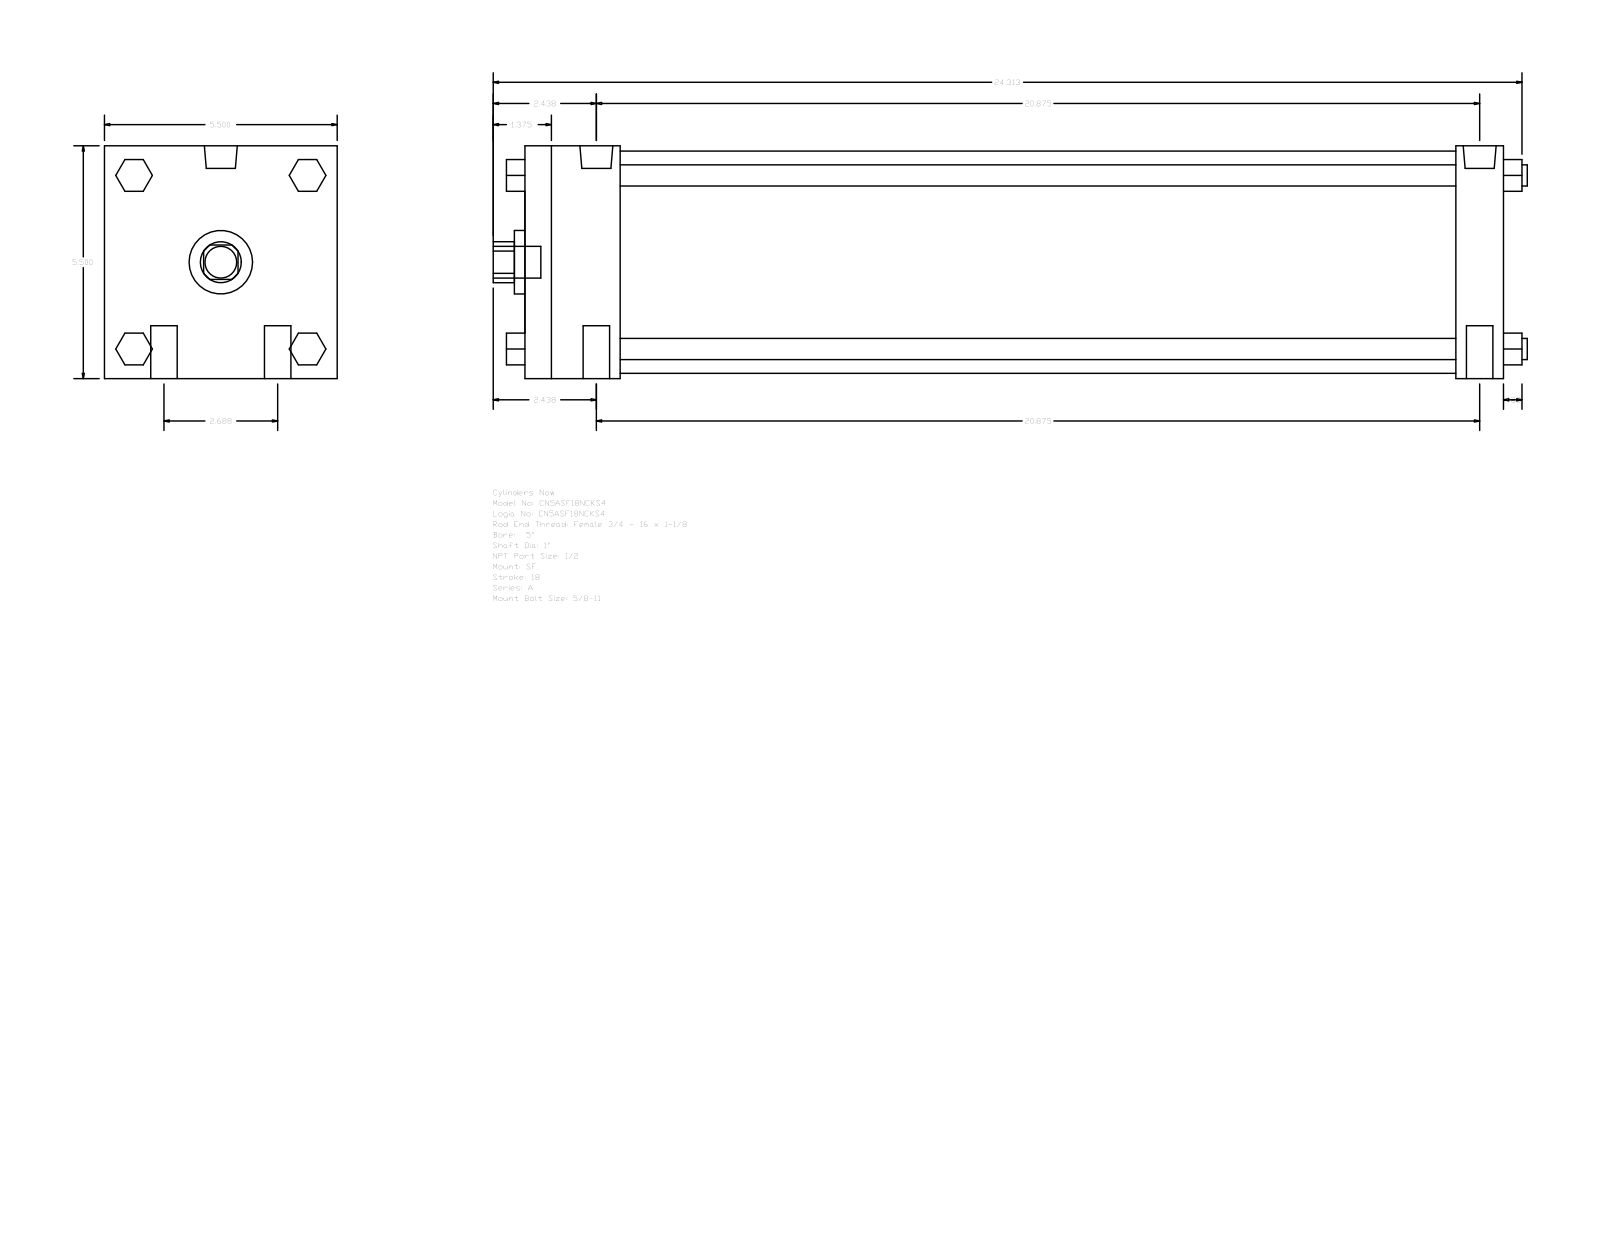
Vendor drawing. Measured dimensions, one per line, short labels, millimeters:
name: A_SF__0500_1
written by: GSSL Pune (CONFIG_CONTROL_DESIGN)
unit: mm
bodies: 0 solids, 124 faces (94 planar, 30 cylindrical, 0 other)
size: 620.71 × 139.7 × 139.7
holes: 1× ⌀25.4, 1× ⌀38.1, 1× ⌀133.35
bosses: 4× ⌀15.88, 4× ⌀12.7, 2× ⌀19.77, 2× ⌀8.73, 1× ⌀19.05
rounds: 1× R12.29
face distances: 139.7, 587.37, 28.57, 57.15, 558.8, 501.65, 530.22, 19.05, 52.07, 90.18
